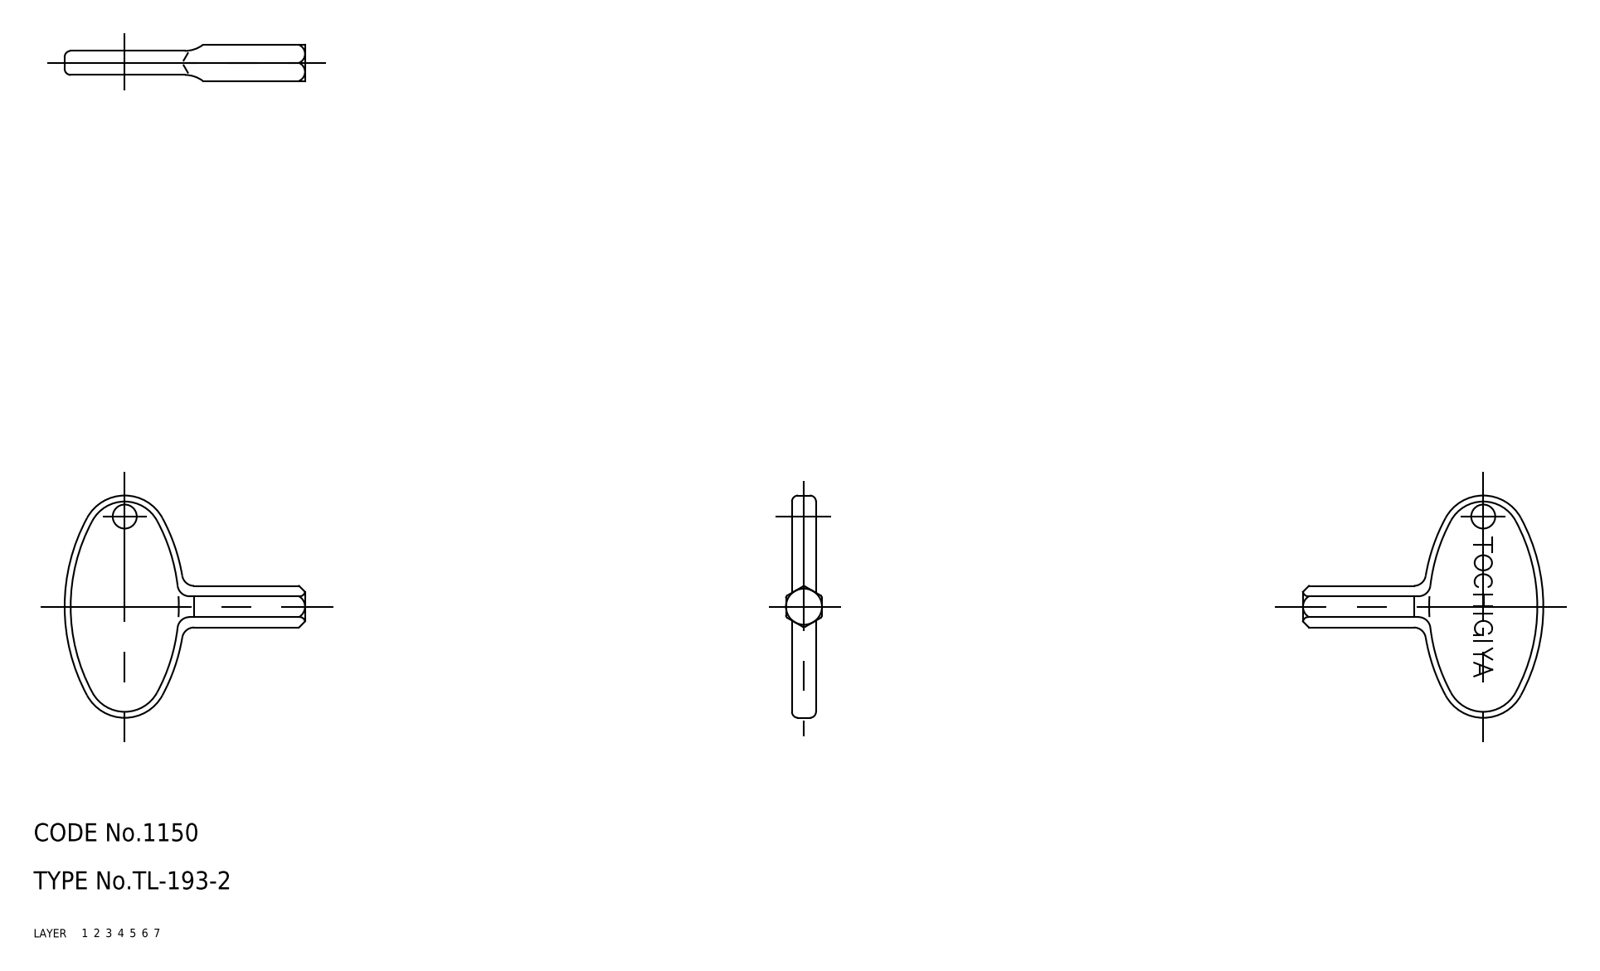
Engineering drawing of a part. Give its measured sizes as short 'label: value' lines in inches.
name: key
written by: CADfix (AUTOMOTIVE_DESIGN)
unit: in
bodies: 1 solid, 46 faces (0 planar, 0 cylindrical, 46 other)
size: 1.575 × 1.457 × 0.236
volume: 0.175 in³; area: 2.943 in²
